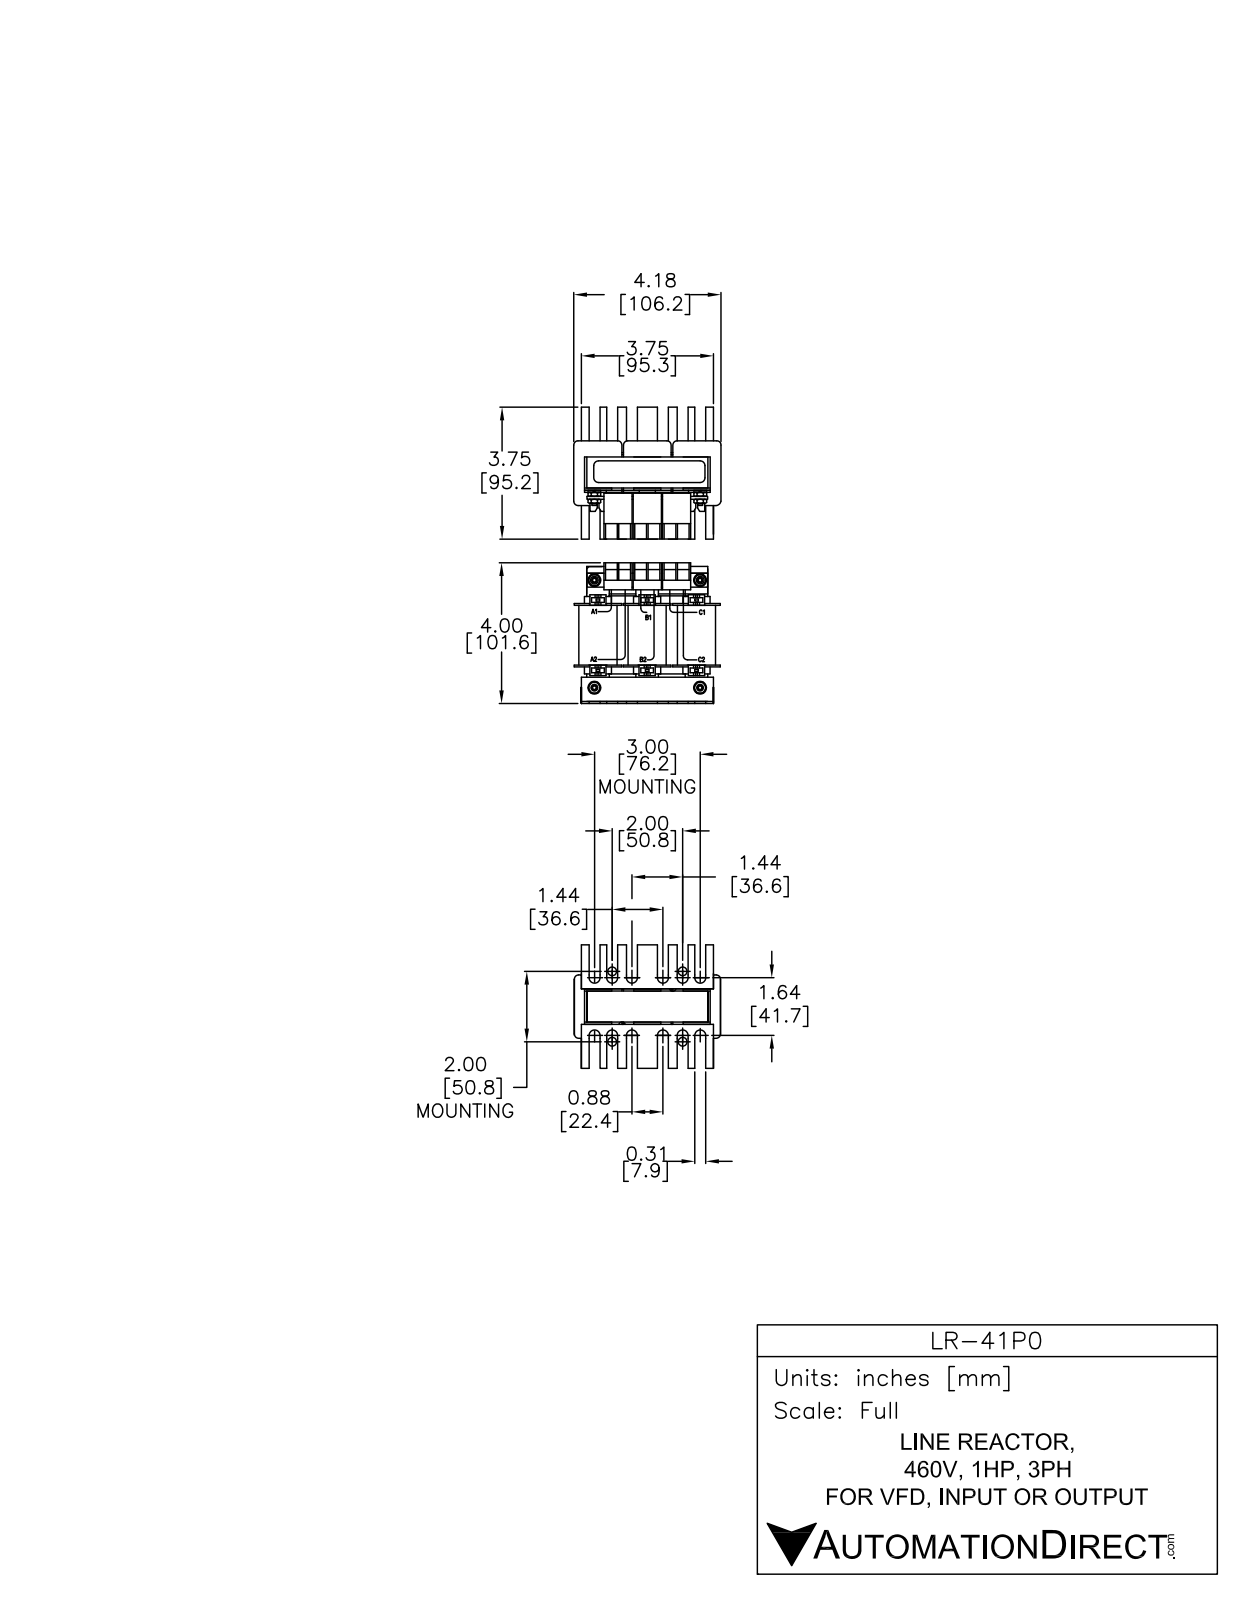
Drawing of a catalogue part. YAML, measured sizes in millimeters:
part_name: "LR-41P0"
step_written_by: "SolidWorks 2011 (AUTOMOTIVE_DESIGN)"
units: millimeters
bodies: {solids: 17, faces: 941, planar: 743, cylindrical: 198, other: 0}
overall_size: [105.25, 98.41, 89.25]
volume: 272326
surface_area: 99223
round_bosses_or_shafts:
  - {diameter: 7.75, count: 4}
  - {diameter: 3.5, count: 4}
partial_cylinders:
  - {radius: 4, count: 50}
  - {radius: 1.82, count: 24}
  - {radius: 8, count: 12}
  - {radius: 3, count: 6}
  - {radius: 0.86, count: 3}
  - {radius: 1.25, count: 2}
face_to_face_distances: [5, 21.5, 2.75, 51, 26.25, 26.5, 7.5, 29, 71, 2.5]
